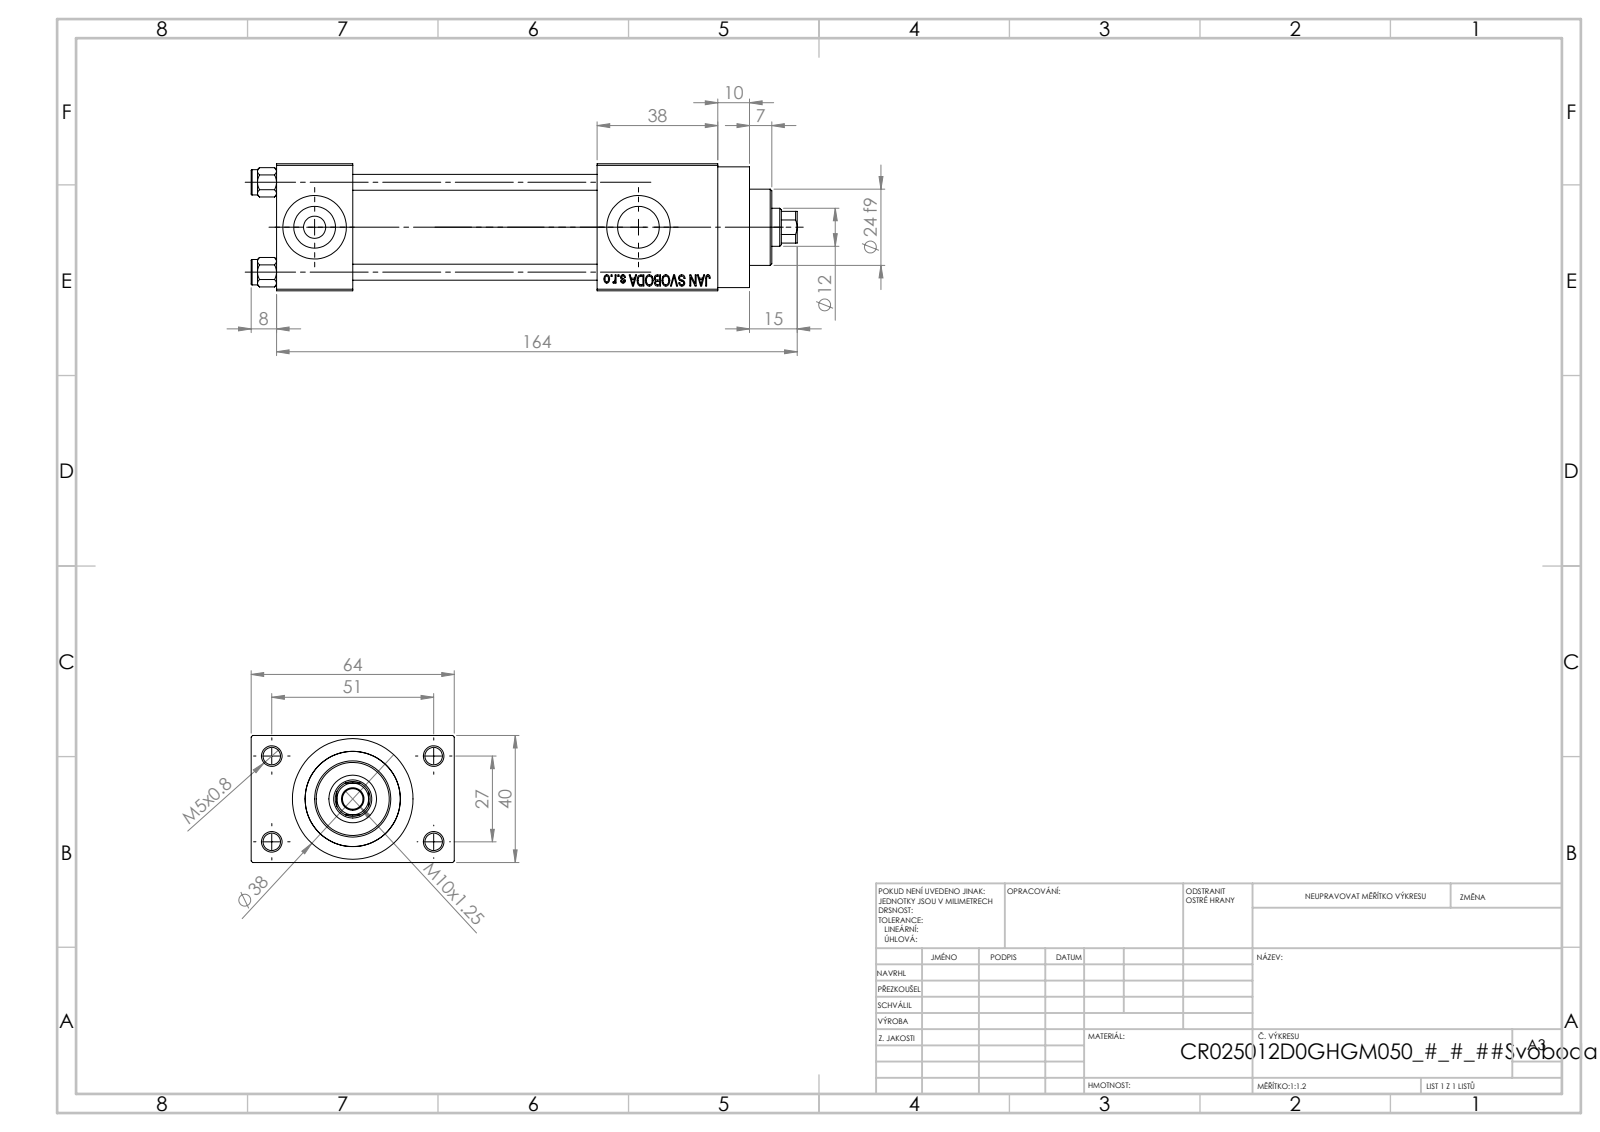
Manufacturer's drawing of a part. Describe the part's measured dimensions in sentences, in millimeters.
The part is named "V215_VC_A; V215CR_D_Body; V215CR_D_TYCINKA; NUT_M5_D (+1 more)". Its 3-D file was written by "SolidWorks 2019 (CONFIG_CONTROL_DESIGN)". It is 11 solids with 1102 faces: 496 planar, 88 cylindrical and 518 other. Overall it measures 172 by 64 by 40 millimeters. Its volume is 187 349 cubic millimeters and its surface area 70 454 square millimeters. Round holes: 4 of diameter 5, 4 of diameter 5.5, 3 of diameter 20, 2 of diameter 7, 2 of diameter 13.16, 1 of diameter 6.5, 1 of diameter 12, 1 of diameter 15, 1 of diameter 25, 1 of diameter 30. Round bosses or shafts: 4 of diameter 8, 1 of diameter 38, 1 of diameter 31, 1 of diameter 24. Partial cylindrical surfaces (rounded edges, fillets, slot ends): 1 of radius 5.5. The main face-to-face distances are 40, 12, 77, 24, 101, 52, 38, 139, 115, 64. The hole center spacings are 11.37, 20.01, 28.3, 28.85, 29.89, 39.66, 48.34, 27.
